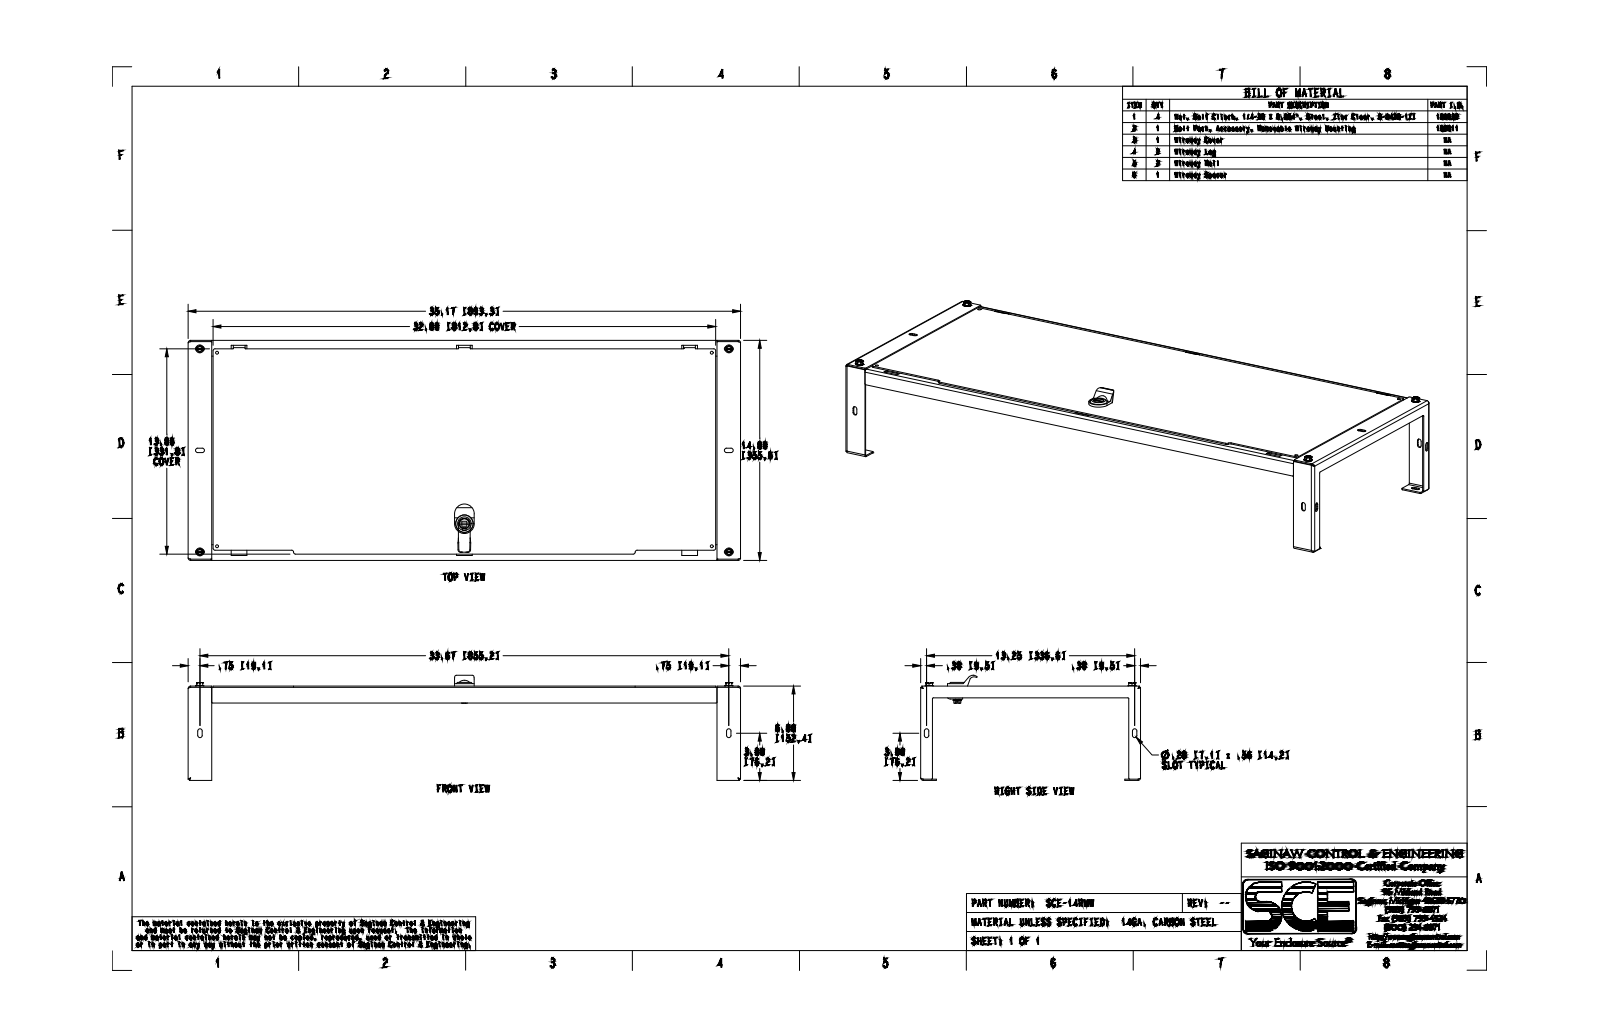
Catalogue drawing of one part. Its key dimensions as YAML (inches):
part_name: "SCE-14RMW"
step_written_by: "SolidWorks 2019 (AUTOMOTIVE_DESIGN)"
units: inches
bodies: {solids: 20, faces: 962, planar: 488, cylindrical: 330, other: 144}
overall_size: [35.17, 14.001, 6.688]
volume: 52.16
surface_area: 1362
round_holes:
  - {diameter: 0.187, count: 4}
  - {diameter: 0.25, count: 4}
  - {diameter: 0.308, count: 4}
  - {diameter: 0.343, count: 4}
  - {diameter: 0.197, count: 1}
  - {diameter: 0.315, count: 1}
  - {diameter: 0.394, count: 1}
  - {diameter: 0.634, count: 1}
  - {diameter: 0.802, count: 1}
  - {diameter: 0.84, count: 1}
  - {diameter: 1.115, count: 1}
round_bosses_or_shafts:
  - {diameter: 0.5, count: 4}
  - {diameter: 0.44, count: 4}
  - {diameter: 0.248, count: 4}
  - {diameter: 1.102, count: 1}
  - {diameter: 0.866, count: 1}
  - {diameter: 0.78, count: 1}
  - {diameter: 0.63, count: 1}
  - {diameter: 0.531, count: 1}
partial_cylinders:
  - {radius: 0.01, count: 40}
  - {radius: 0.012, count: 30}
  - {radius: 0.015, count: 24}
  - {radius: 0.141, count: 24}
  - {radius: 0.06, count: 16}
  - {radius: 0.125, count: 14}
  - {radius: 0.02, count: 10}
  - {radius: 0.03, count: 4}
face_to_face_distances: [0.078, 0.078, 13.922, 0.078, 0.156, 14, 13.844, 0.156, 13.922, 13.922]
hole_center_spacings: [12.313, 12.608, 12.717, 12.918, 15.815, 19.14, 31.5, 33.821]
